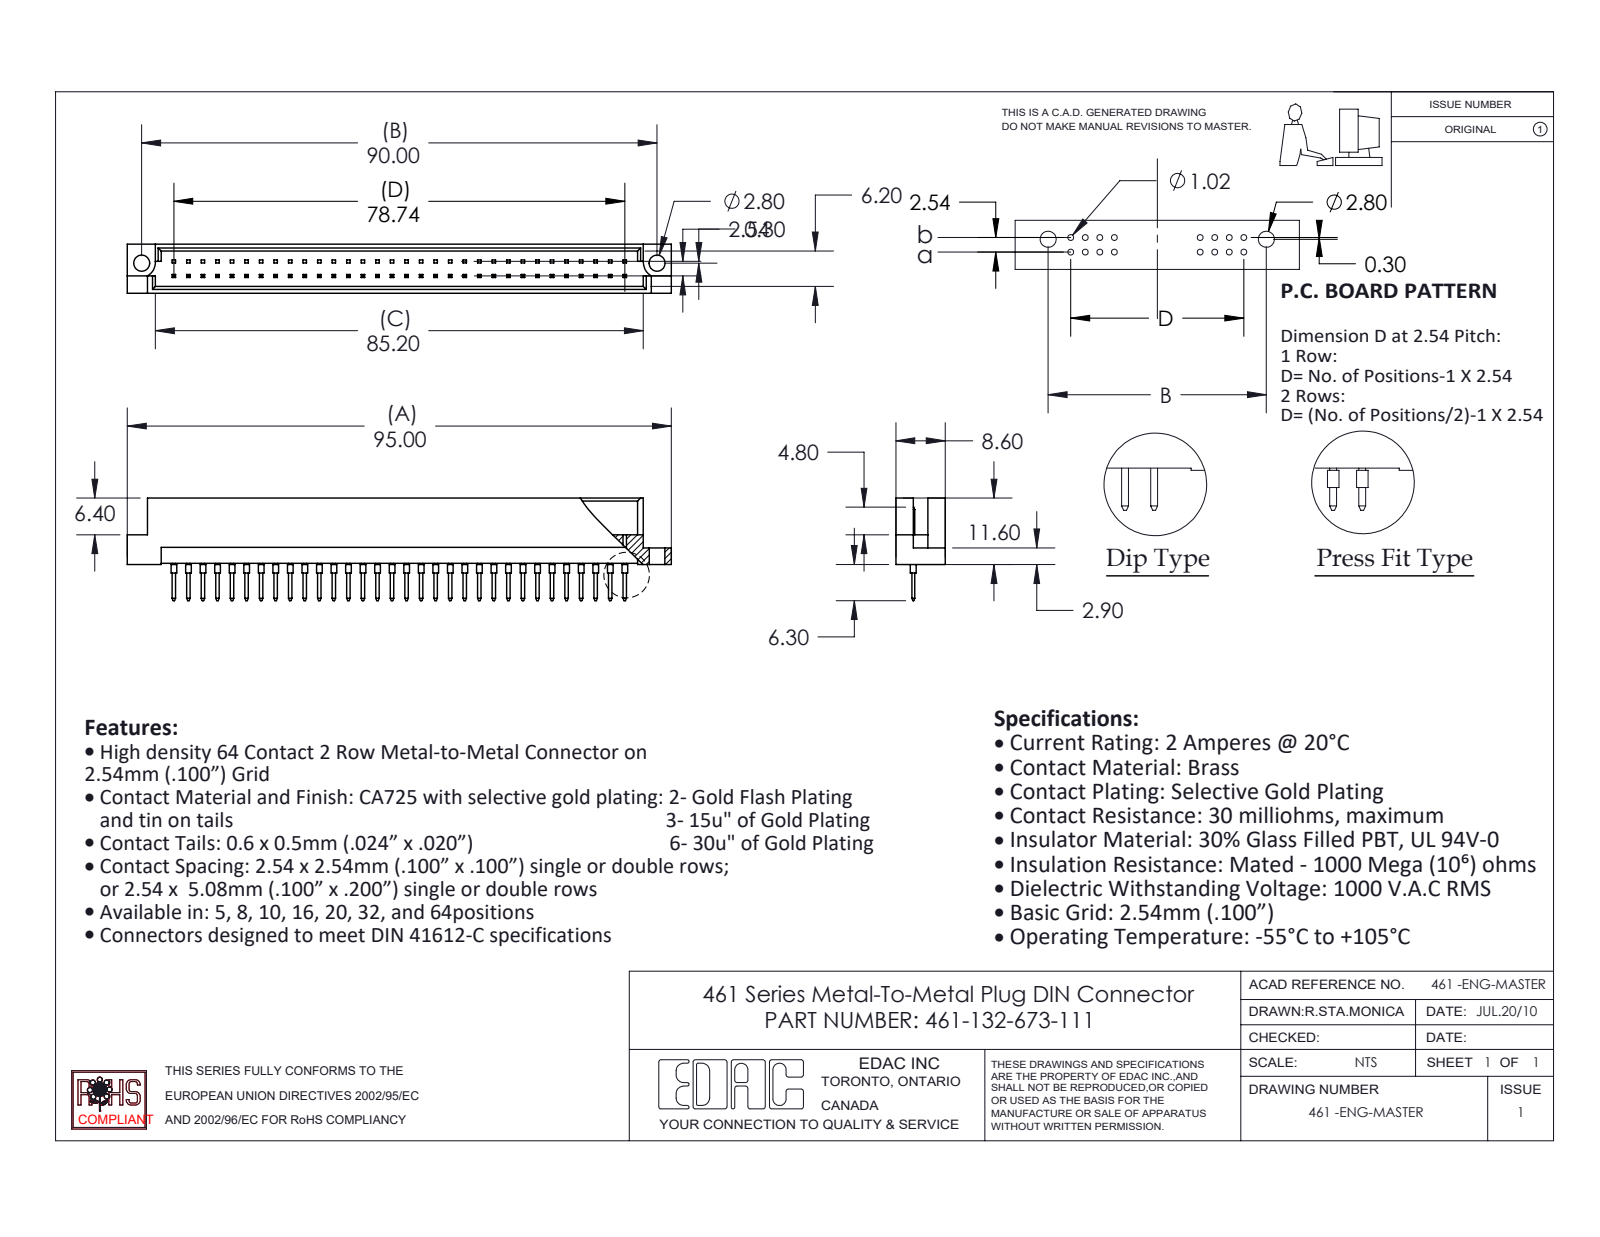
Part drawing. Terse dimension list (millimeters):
name: 461-132-673-111; 461 Part_64; 461-290_73
written by: SolidWorks 2020 (CONFIG_CONTROL_DESIGN)
unit: mm
bodies: 33 solids, 1009 faces (938 planar, 71 cylindrical, 0 other)
size: 95 × 17.9 × 8.6
volume: 4 833 mm³; area: 6 883 mm²
holes: 2× ⌀2.8
bosses: 32× ⌀1
rounds: 2× R2.8
face distances: 1.2, 7.4, 8.6, 6.2, 5, 3.28, 5.32, 2.08, 4.12, 2.78
hole spacings: 90
